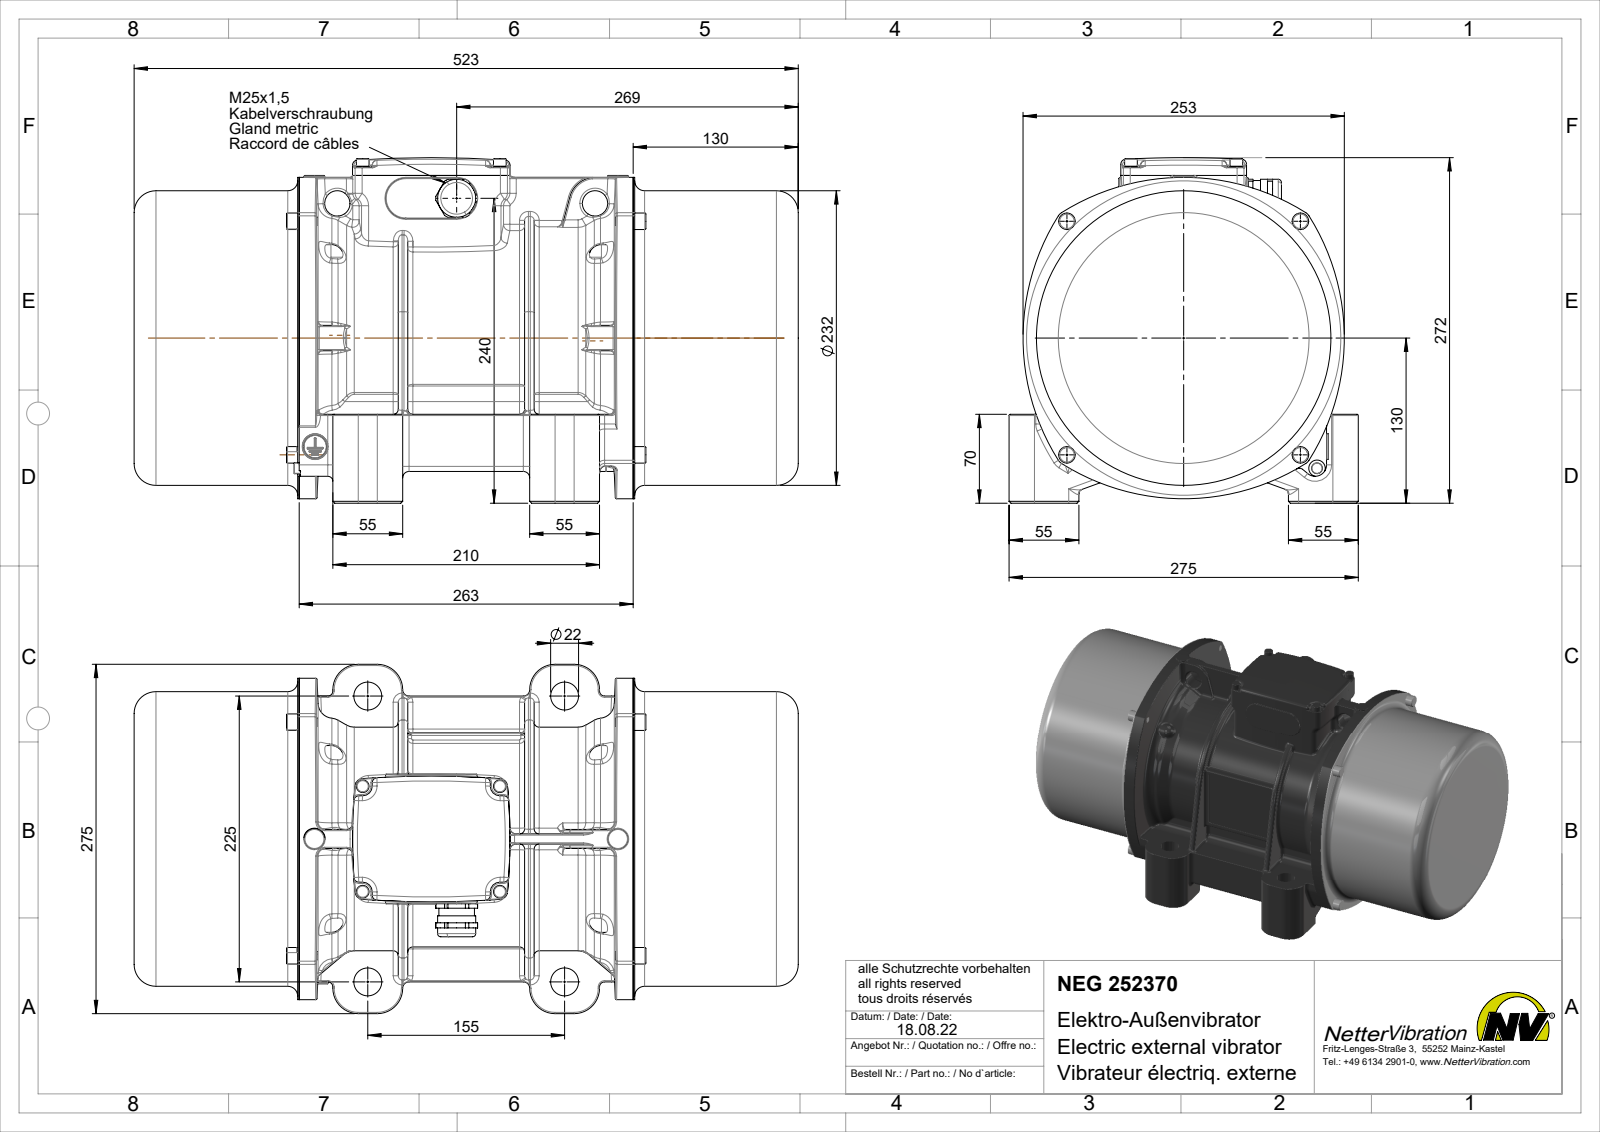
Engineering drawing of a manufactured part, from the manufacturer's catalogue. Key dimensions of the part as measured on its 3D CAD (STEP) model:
Part name (STEP PRODUCT): NEG 252370 50-60Hz
STEP written by: SolidWorks 2015 (AUTOMOTIVE_DESIGN)
Units: millimetres
Bodies: 6 solids, 2659 faces (446 planar, 647 cylindrical, 1566 other)
Overall size (bounding box): 523 × 275 × 272
Volume: 19 610 000 mm³ · Surface area: 1 270 000 mm²
Round holes (diameter × count): ⌀22 ×4, ⌀20 ×2, ⌀100.5 ×2, ⌀13 ×1, ⌀18 ×1, ⌀25 ×1, ⌀110 ×1, ⌀114 ×1, ⌀152 ×1, ⌀210 ×1, ⌀243 ×1
Round bosses / shafts (diameter × count): ⌀10 ×8, ⌀16 ×4, ⌀13 ×4, ⌀8 ×4, ⌀6 ×4, ⌀5 ×2, ⌀231.9 ×1, ⌀165 ×1
Partial cylindrical surfaces — rounded edges, fillets, slot ends (radius × count): R0.2 ×102, R5 ×56, R4 ×55, R1 ×24, R3 ×20, R2 ×18, R8 ×17, R10 ×10
Main face-to-face distances: 133.5, 389.5, 130, 3.5, 393, 259.5, 523, 256, 263, 55
Hole centre spacings: 136.61, 2.25, 155, 225, 273.22, 4.48, 20.16, 116.92
